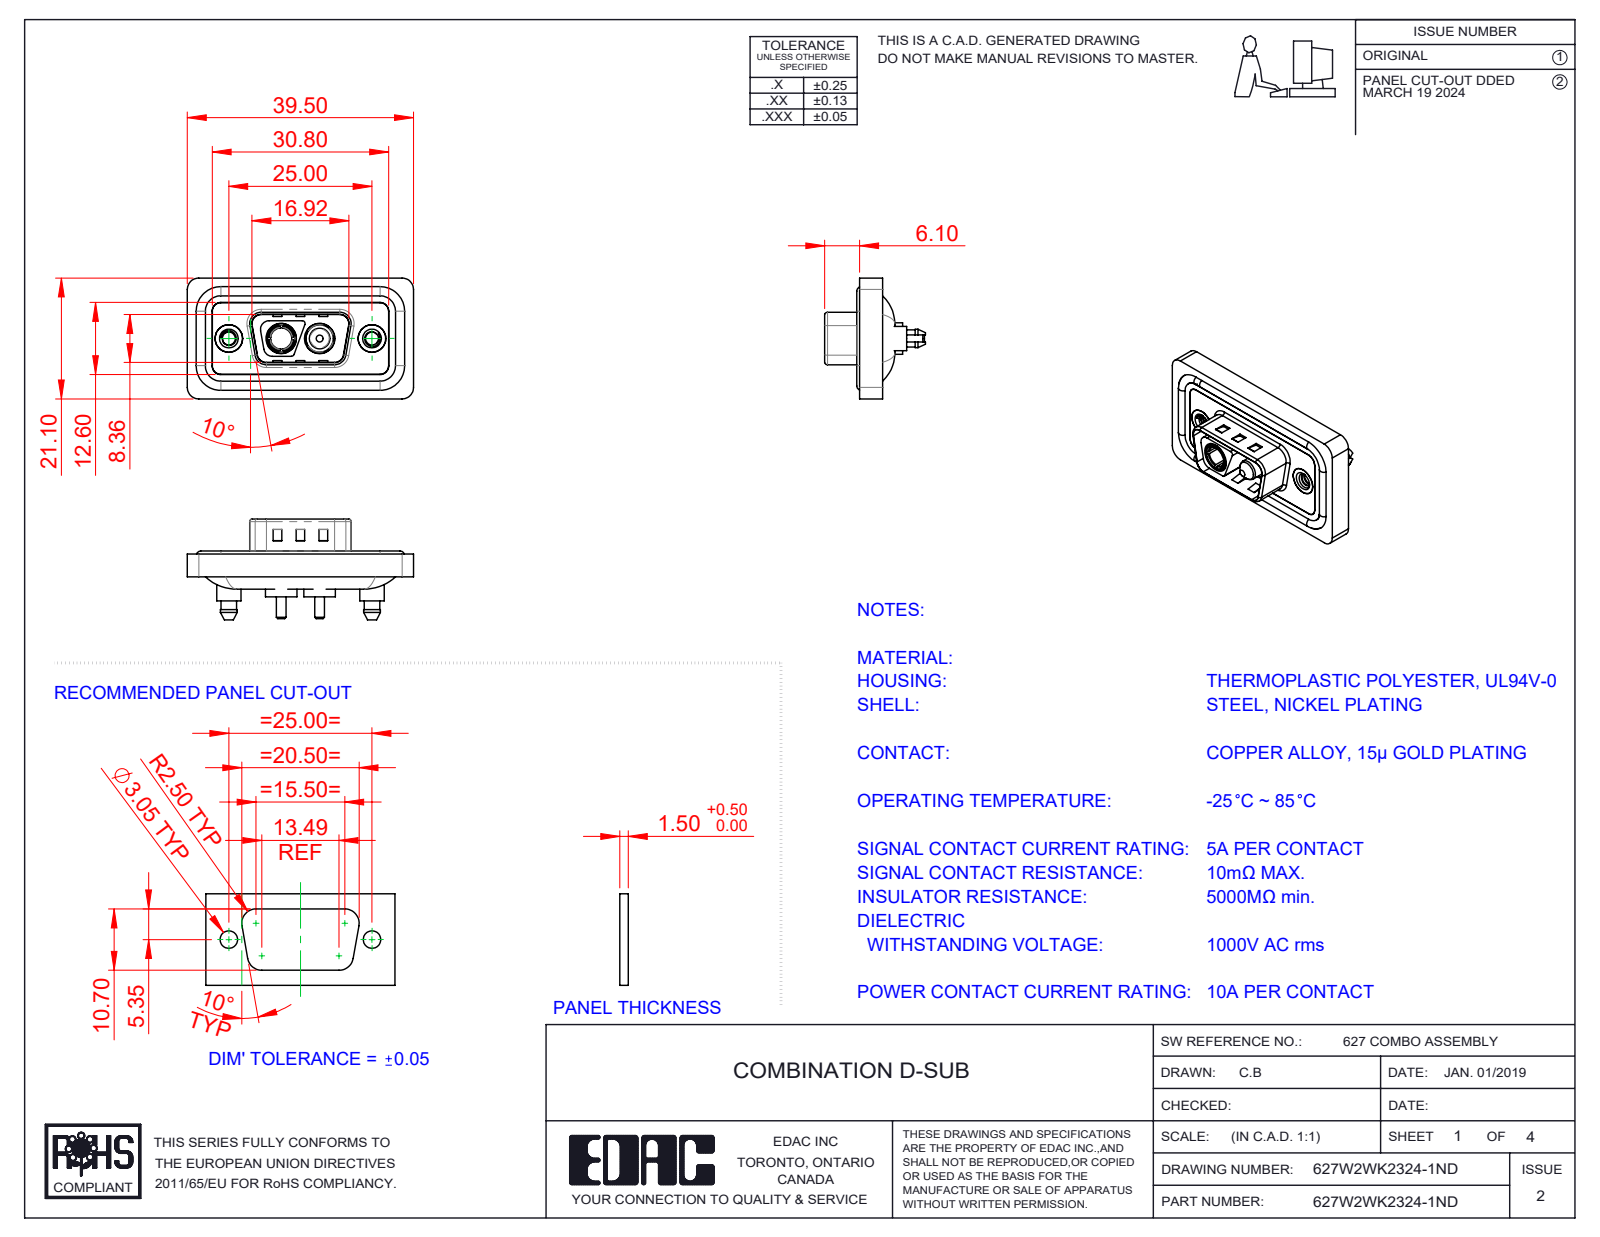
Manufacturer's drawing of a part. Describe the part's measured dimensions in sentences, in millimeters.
The part is named "627Combo Threaded Boardlock_D; Power Pin_10A S; 627Combo Waterproof Housing_09 Contacts; 627Combo Threaded Boardlock_5 (+5 more)". Its 3-D file was written by "SolidWorks 2023 (CONFIG_CONTROL_DESIGN)". It is 11 solids with 592 faces: 205 planar, 267 cylindrical and 120 other. Overall it measures 39.5 by 21.1 by 17.6 millimeters. Its volume is 4 659 cubic millimeters and its surface area 7 653 square millimeters. Round holes: 2 of diameter 2.26, 2 of diameter 4, 2 of diameter 4.8, 2 of diameter 4.85, 2 of diameter 5, 2 of diameter 5.3, 1 of diameter 3.7. Round bosses or shafts: 4 of diameter 1.6, 2 of diameter 5.5, 2 of diameter 5.4, 2 of diameter 5.2, 2 of diameter 4.9, 2 of diameter 4.75, 2 of diameter 4.25, 2 of diameter 3.75. Partial cylindrical surfaces (rounded edges, fillets, slot ends): 26 of radius 1.5, 18 of radius 2, 10 of radius 0.5, 10 of radius 1.6, 4 of radius 0.25, 4 of radius 0.6, 4 of radius 0.65, 4 of radius 0.9. The main face-to-face distances are 0.4, 1.1, 2.9, 0.5, 1.6, 3.1, 1.5, 4, 1.8, 3.2. The hole center spacings are 9.14, 15.86, 6.72, 25.
